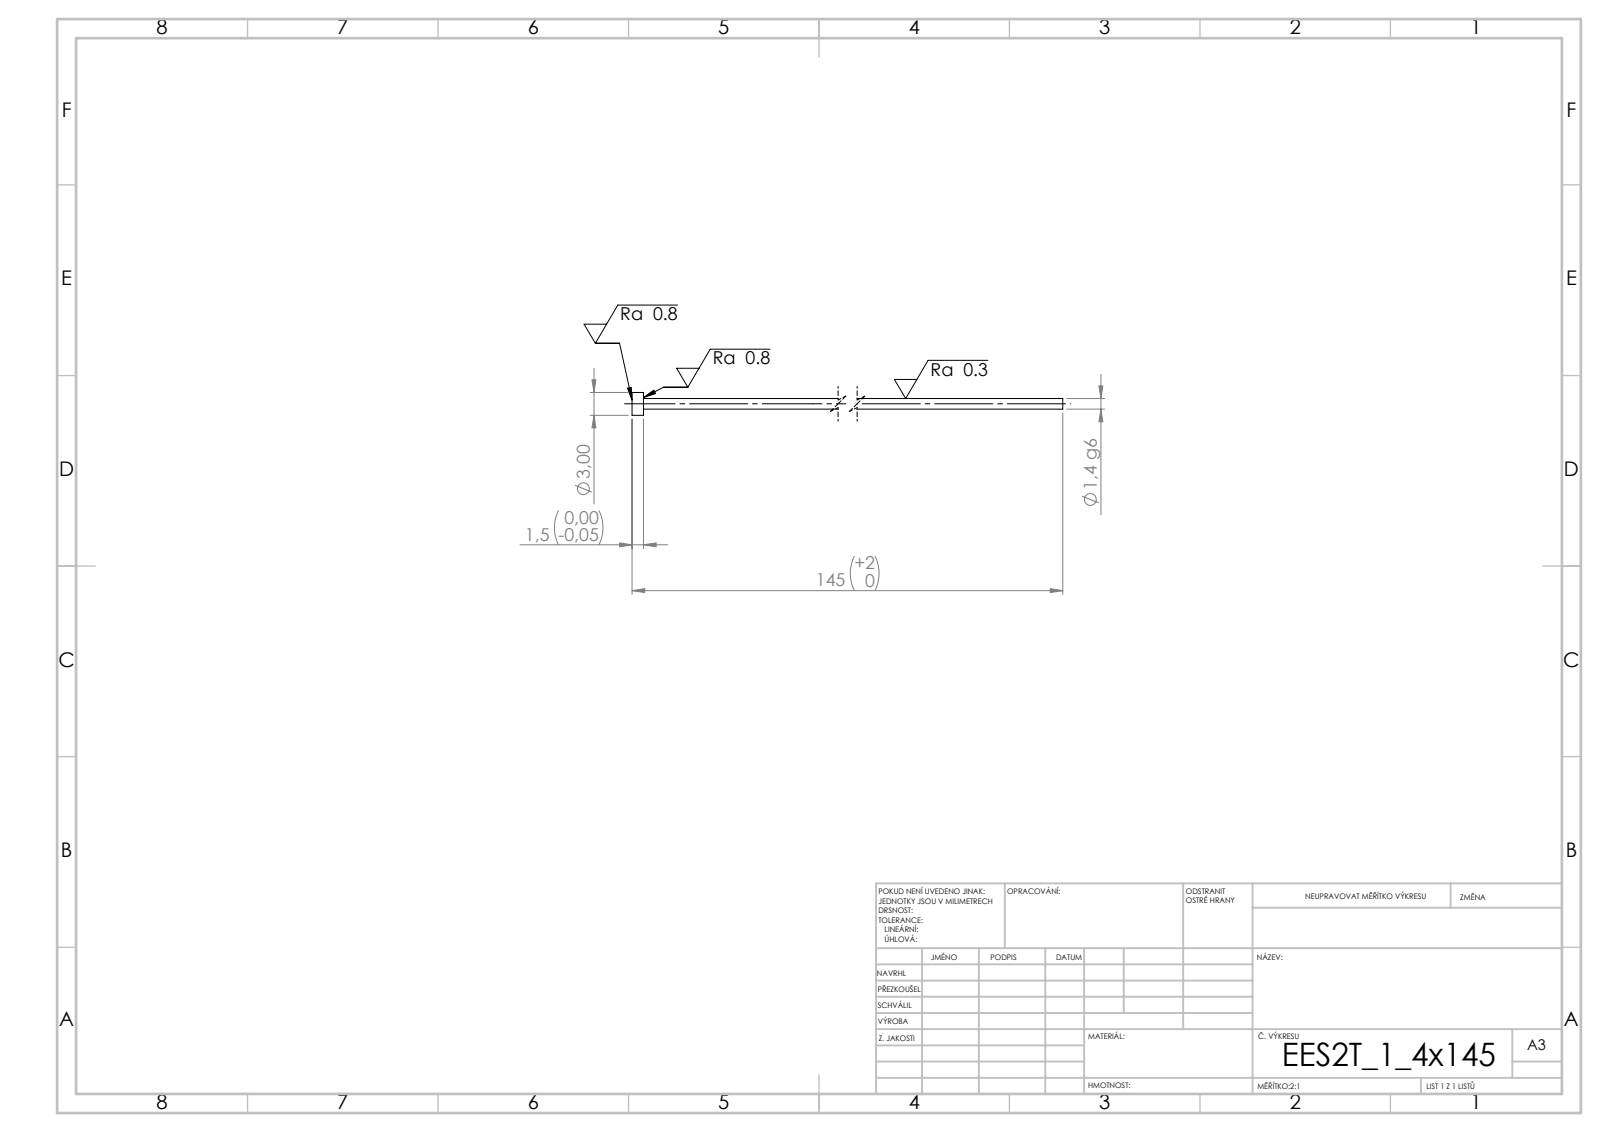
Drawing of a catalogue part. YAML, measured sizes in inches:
step_written_by: "SolidWorks 2019 (CONFIG_CONTROL_DESIGN)"
units: inches
bodies: {solids: 1, faces: 7, planar: 3, cylindrical: 4, other: 0}
overall_size: [5.709, 0.118, 0.118]
volume: 0.014
surface_area: 1.02
round_bosses_or_shafts:
  - {diameter: 0.118, count: 1}
  - {diameter: 0.055, count: 1}
face_to_face_distances: [0.059, 5.709, 5.65]
